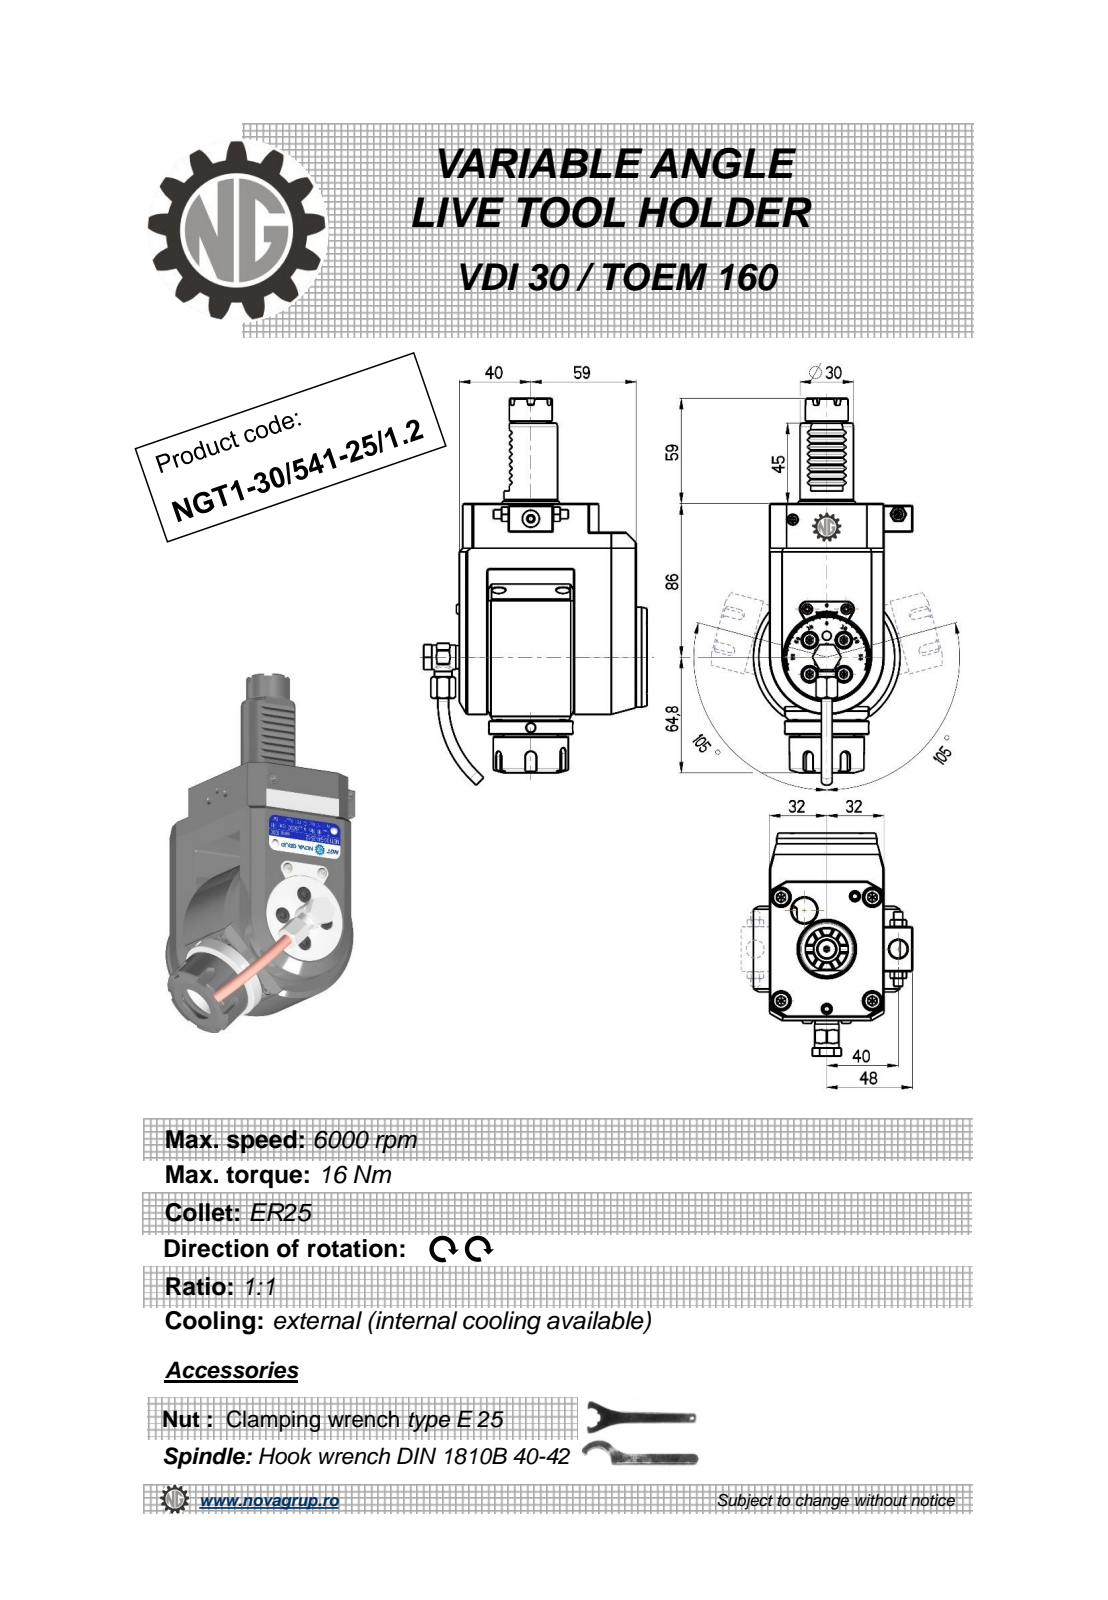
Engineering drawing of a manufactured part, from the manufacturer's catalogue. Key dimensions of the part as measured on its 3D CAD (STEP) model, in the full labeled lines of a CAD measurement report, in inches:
Part name (STEP PRODUCT): NGT1_30_541_25_1_2
STEP written by: PRO/ENGINEER BY PARAMETRIC TECHNOLOGY CORPORATION, 2010280 (CONFIG_CONTROL_DESIGN)
Units: inches
Bodies: 1 solid, 571 faces (244 planar, 130 cylindrical, 197 other)
Overall size (bounding box): 8.53 × 4.917 × 3.504
Volume: 47.81 in³ · Surface area: 117.1 in²
Round holes (diameter × count): ⌀0.157 ×3, ⌀0.197 ×2, ⌀0.394 ×2, ⌀0.118 ×1, ⌀0.165 ×1, ⌀0.177 ×1, ⌀0.244 ×1, ⌀0.354 ×1, ⌀0.374 ×1, ⌀0.433 ×1, ⌀0.799 ×1
Round bosses / shafts (diameter × count): ⌀0.236 ×2, ⌀0.224 ×2, ⌀3.228 ×1, ⌀2.205 ×1, ⌀1.85 ×1, ⌀1.654 ×1, ⌀1.378 ×1, ⌀1.181 ×1
Partial cylindrical surfaces — rounded edges, fillets, slot ends (radius × count): R0.01 ×12, R0.012 ×8, R0.118 ×5, R0.02 ×4, R0.039 ×2, R0.303 ×1, R1.26 ×1
Main face-to-face distances: 2.52, 0.63, 1.457, 0.236, 3.898, 4.134, 0.551, 3.268, 2.441, 0.827
Hole centre spacings: 0.016, 1.553, 1.575, 1.929, 1.945, 2.49, 2.502, 3.521
